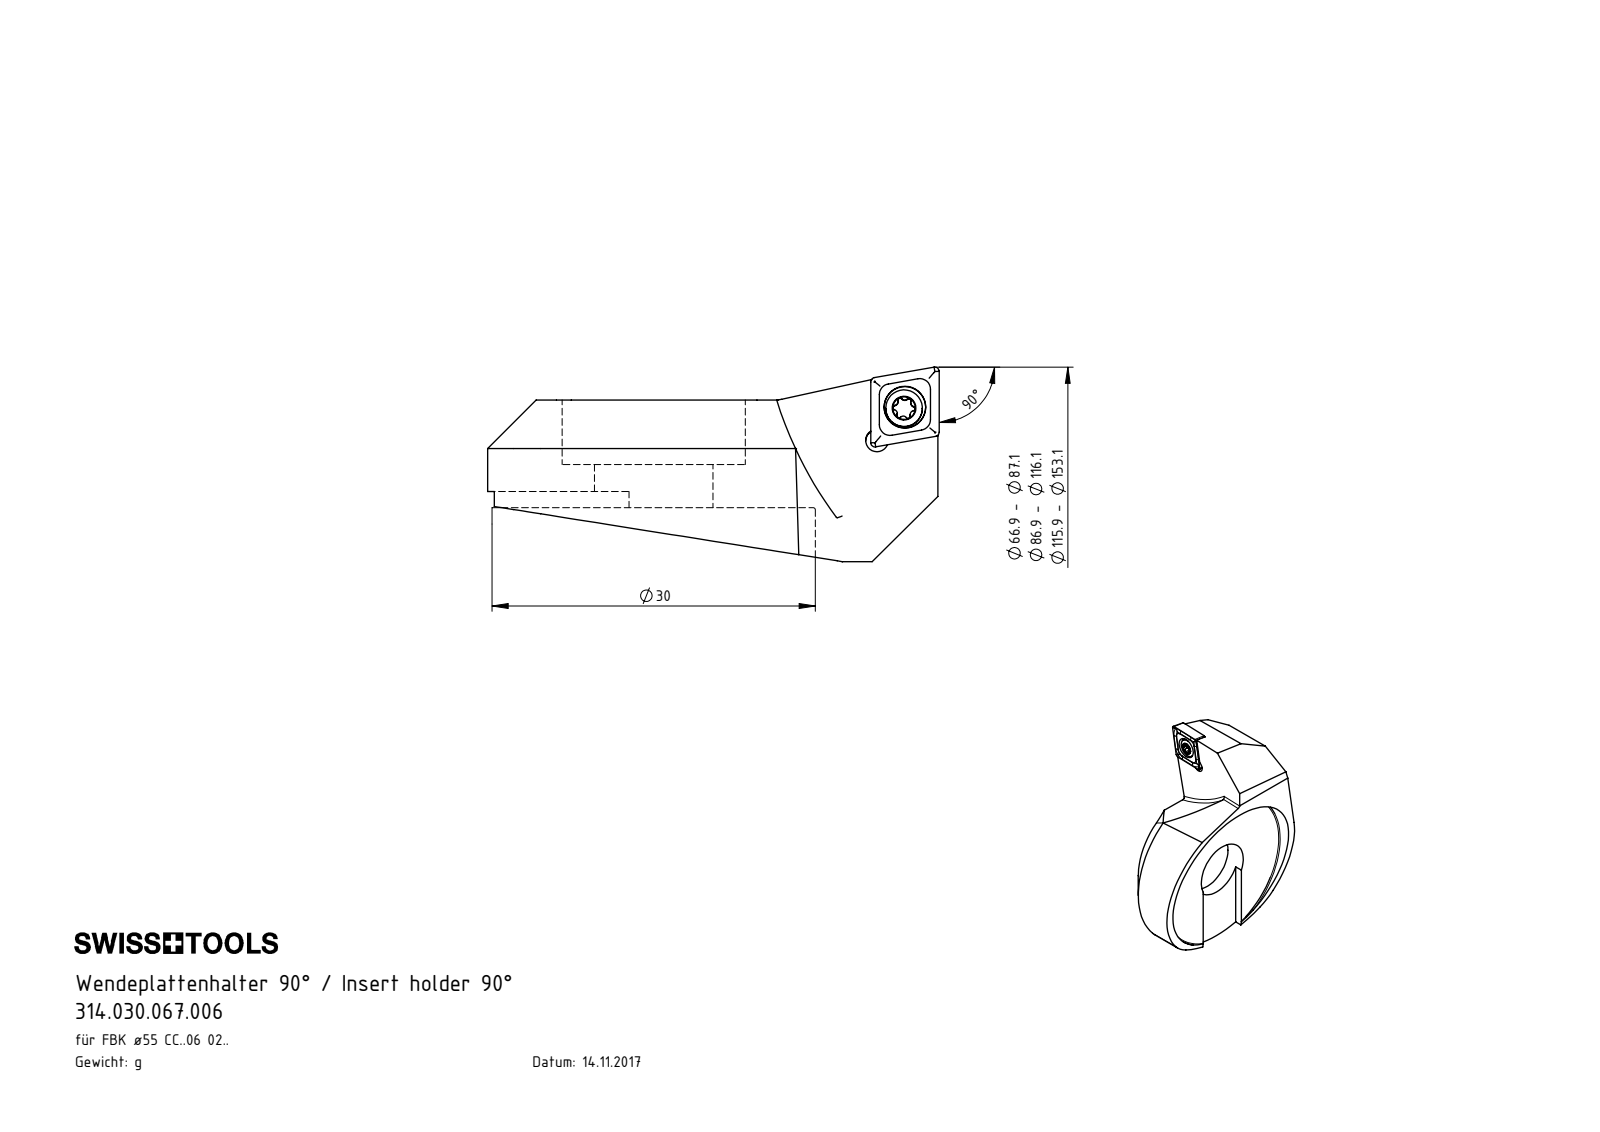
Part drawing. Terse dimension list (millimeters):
name: F55-WCA.001.013_D_fertigbearbeitet; CCMT060204; WCA-ER2.001.005_A; 314.030.067.006
written by: SolidWorks 2017 (CONFIG_CONTROL_DESIGN)
unit: mm
bodies: 5 solids, 153 faces (48 planar, 48 cylindrical, 57 other)
size: 41.9 × 33.1 × 18.05
volume: 8 032 mm³; area: 4 569 mm²
holes: 1× ⌀2.05, 1× ⌀2.1, 1× ⌀2.8, 1× ⌀3.85, 1× ⌀11, 1× ⌀17, 1× ⌀30
bosses: 1× ⌀3.4, 1× ⌀2.5
rounds: 6× R0.21, 5× R0.36, 2× R0.5, 2× R10, 1× R0.36, 1× R1.05, 1× R5, 1× R16.55
face distances: 10, 9, 1, 5, 6, 4, 8.5, 7.5, 2.5, 1.5
hole spacings: 3.91, 4.04
